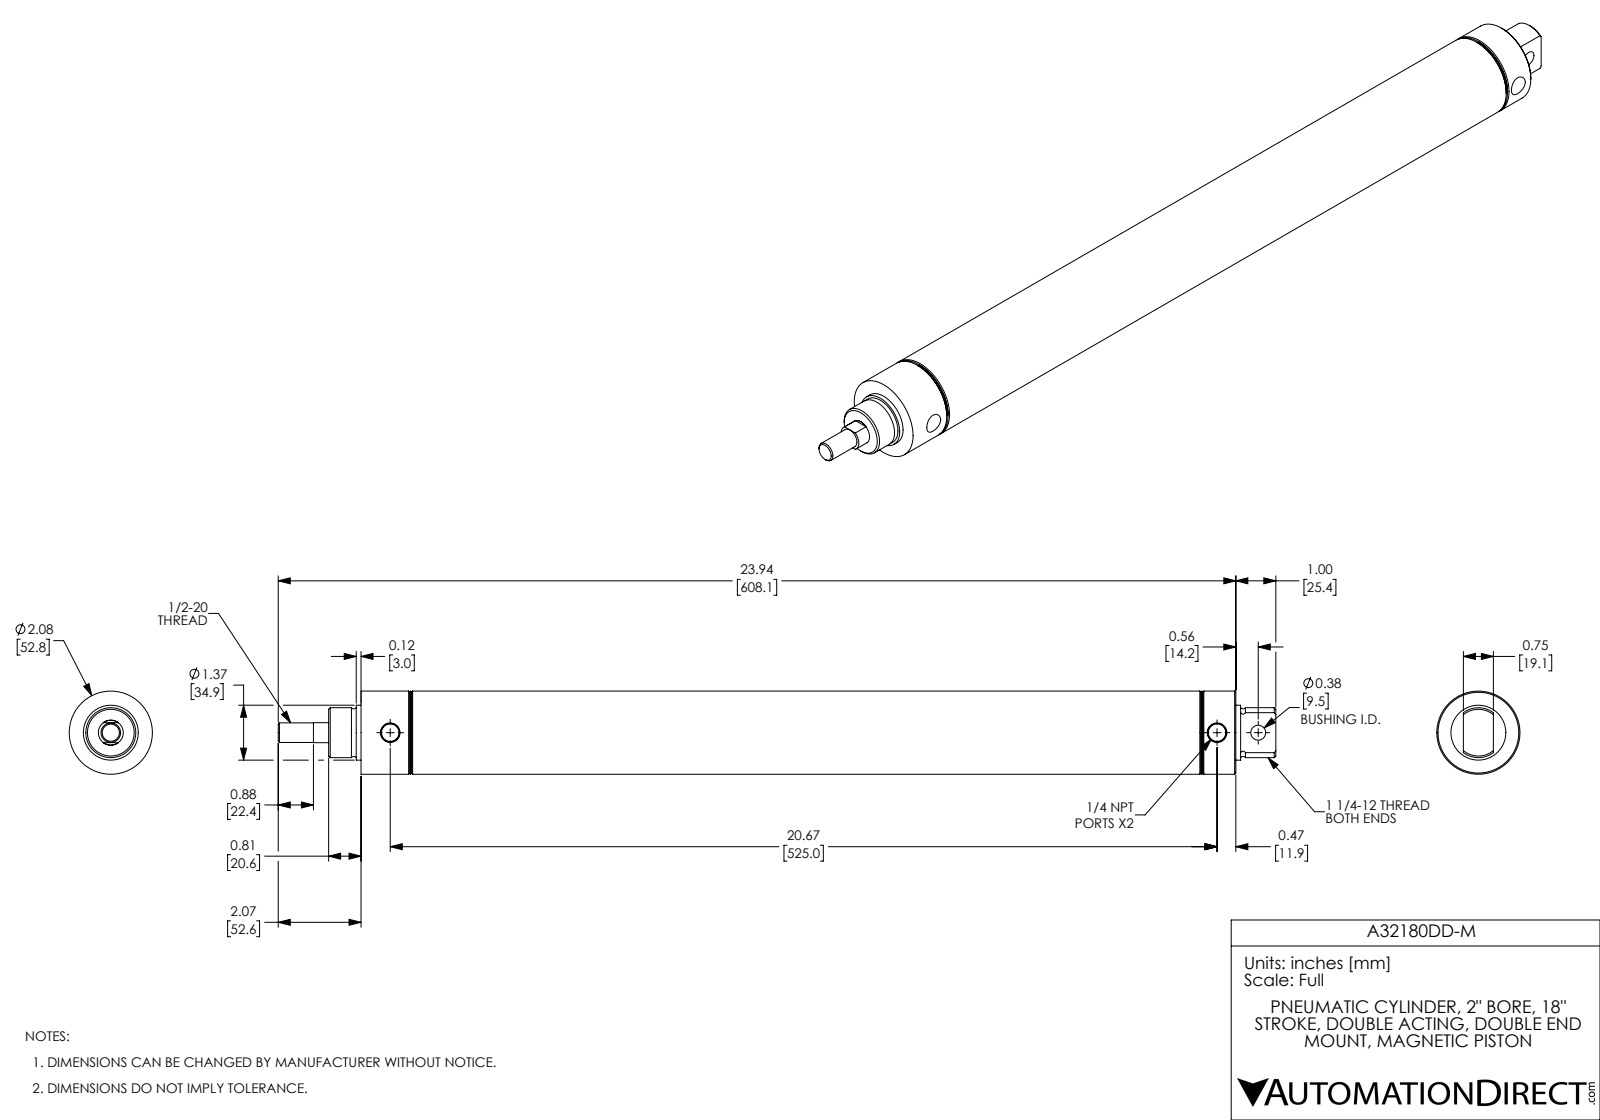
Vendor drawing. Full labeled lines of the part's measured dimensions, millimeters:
Part name (STEP PRODUCT): A32180DD-M-MainBody; A32180DD-M-Rod; A32180DD-M
STEP written by: SolidWorks 2017 (AUTOMOTIVE_DESIGN)
Units: millimetres
Bodies: 2 solids, 88 faces (20 planar, 30 cylindrical, 38 other)
Overall size (bounding box): 633.5 × 52.8 × 52.8
Volume: 411 600 mm³ · Surface area: 218 300 mm²
Round holes (diameter × count): ⌀11.1 ×2, ⌀9.5 ×1, ⌀15.9 ×1, ⌀50.8 ×1
Round bosses / shafts (diameter × count): ⌀52.8 ×1, ⌀34.9 ×1, ⌀31.8 ×1, ⌀12.5 ×1
Main face-to-face distances: 12.7, 469.9, 457.2, 512.7, 500, 42.8, 42.8, 55.5, 512.7, 555.5
Hole centre spacings: 26.2, 525, 551.2
